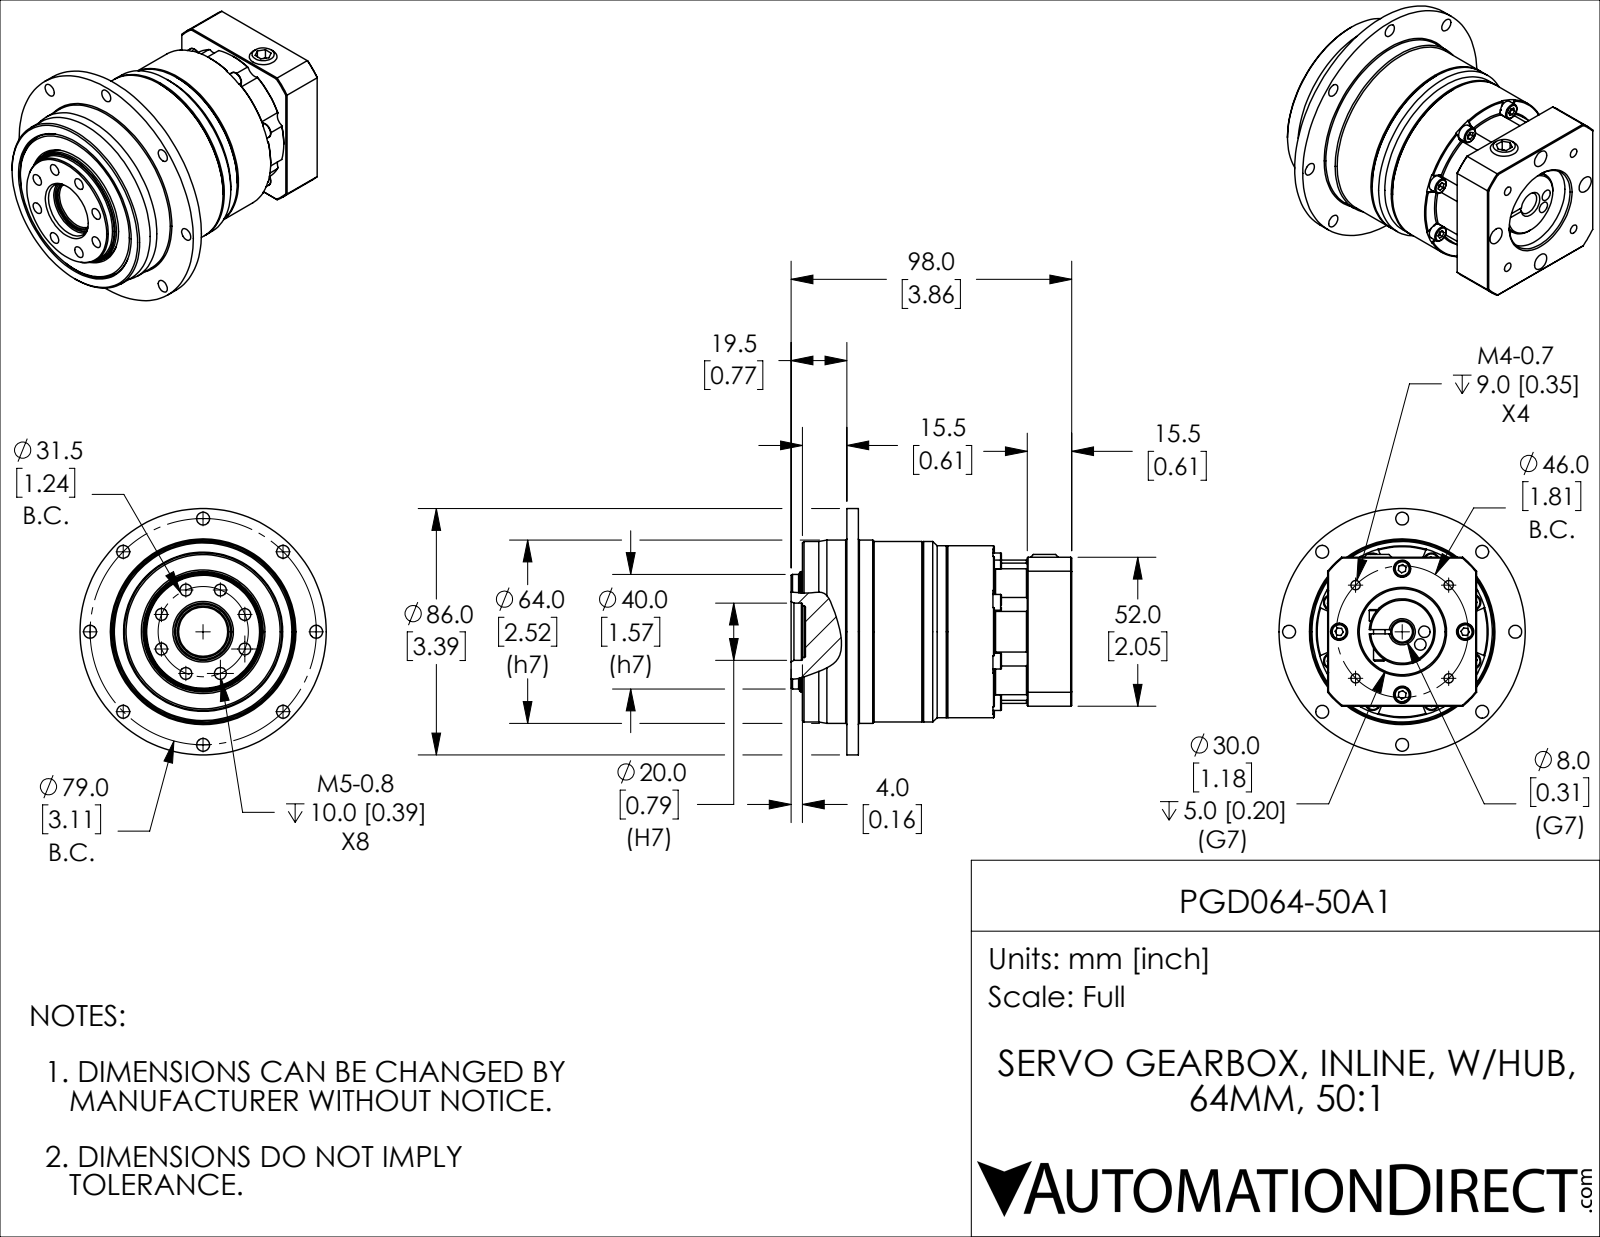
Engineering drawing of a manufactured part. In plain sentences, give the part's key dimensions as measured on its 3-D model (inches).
The part is named "PGD064-50A1". Its 3-D file was written by "SolidWorks 2015 (AUTOMOTIVE_DESIGN)". It is 15 solids with 502 faces: 237 planar, 188 cylindrical and 77 other. Overall it measures 3.858 by 3.386 by 3.386 inches. Its volume is 16.62 cubic inches and its surface area 73.3 square inches. Round holes: 8 of diameter 0.163, 8 of diameter 0.177, 4 of diameter 0.128, 4 of diameter 0.157, 4 of diameter 0.236, 2 of diameter 0.315, 1 of diameter 0.197, 1 of diameter 0.677, 1 of diameter 1.181. Round bosses or shafts: 12 of diameter 0.217, 1 of diameter 3.386, 1 of diameter 2.52, 1 of diameter 2.48, 1 of diameter 2.362, 1 of diameter 1.654, 1 of diameter 1.575, 1 of diameter 0.906. Partial cylindrical surfaces (rounded edges, fillets, slot ends): 8 of radius 0.128, 1 of radius 0.157, 1 of radius 0.972, 1 of radius 0.984, 1 of radius 1.307. The main face-to-face distances are 0.157, 0.387, 0.545, 3.091, 0.079, 0.039, 0.846, 0.689, 0.302, 2.933. The hole center spacings are 1.437, 2.141, 0.62, 0.377, 0.408, 0.679, 0.85, 0.877.
